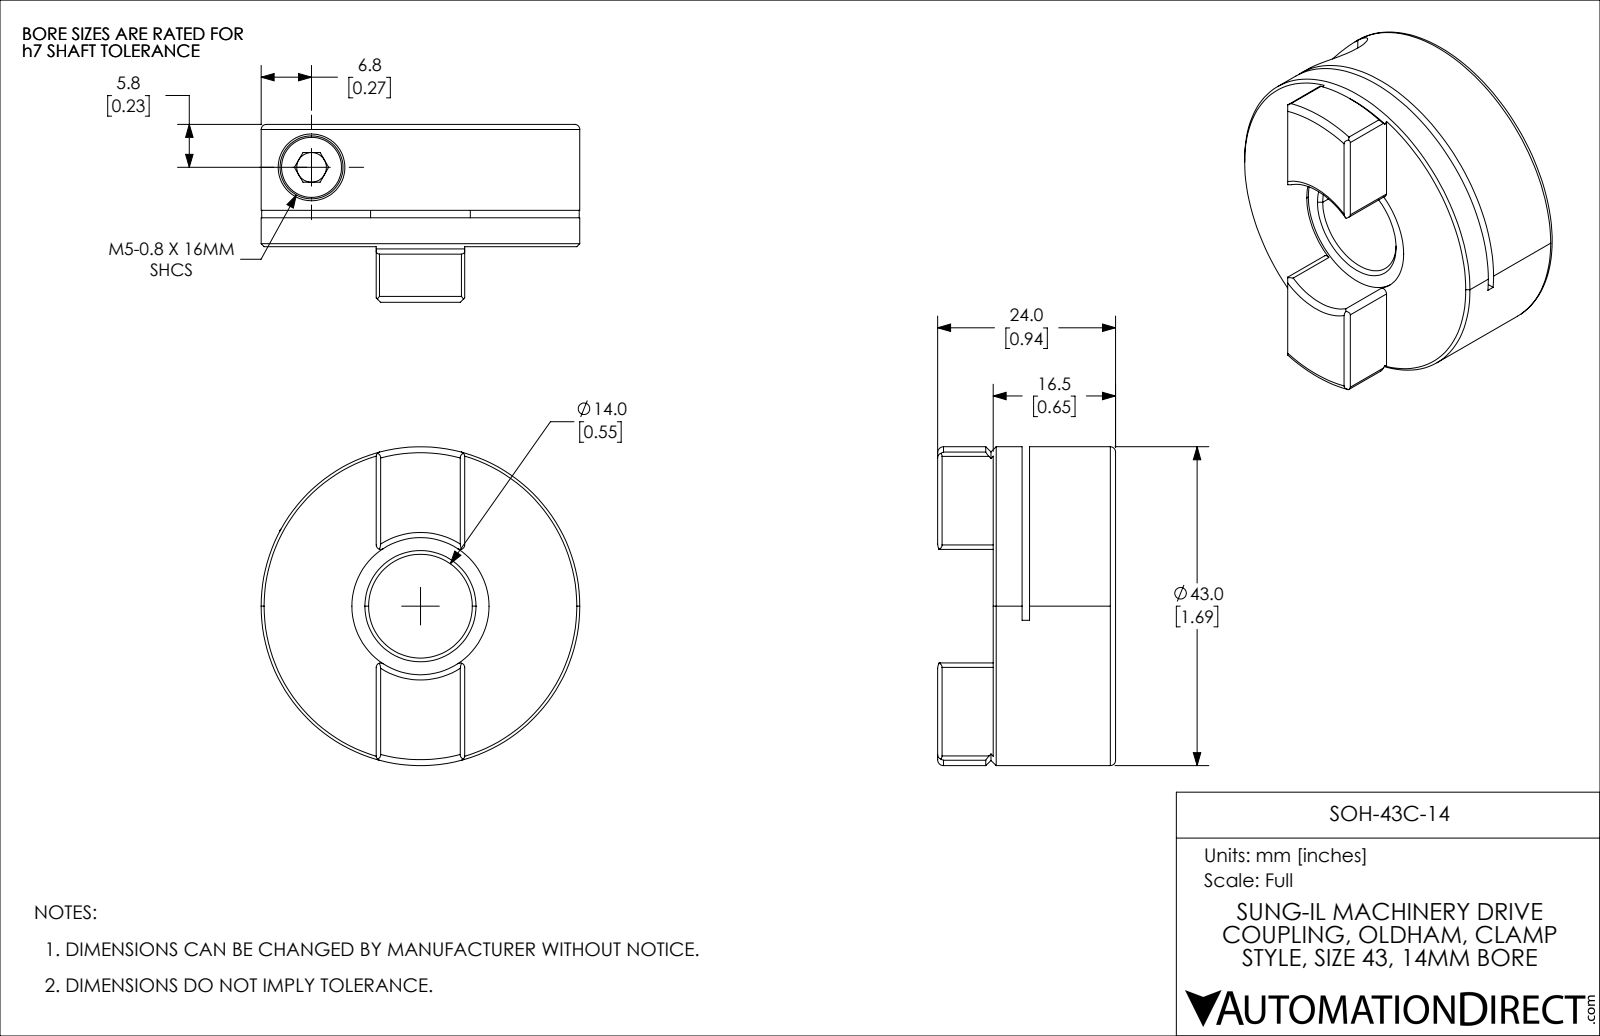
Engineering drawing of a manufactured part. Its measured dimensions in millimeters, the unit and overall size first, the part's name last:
Units: millimetres
Overall size (bounding box): 43 × 43 × 24
Round holes (diameter × count): ⌀4 ×1, ⌀4.2 ×1, ⌀5.4 ×1, ⌀9 ×1, ⌀14 ×1, ⌀18.5 ×1
Round bosses / shafts (diameter × count): ⌀43 ×1, ⌀8.5 ×1, ⌀5 ×1
Partial cylindrical surfaces — rounded edges, fillets, slot ends (radius × count): R0.6 ×8, R37.5 ×1
Main face-to-face distances: 16.5, 12.6, 3.9, 11.6, 1, 4.9, 12.4, 24, 11.4, 7.5
Volume: 22 194 mm³ · Surface area: 8 904 mm²
Bodies: 2 solids, 95 faces (39 planar, 33 cylindrical, 23 other)
Part name (STEP PRODUCT): SOH-43C-14
STEP written by: SolidWorks 2021 (CONFIG_CONTROL_DESIGN)
